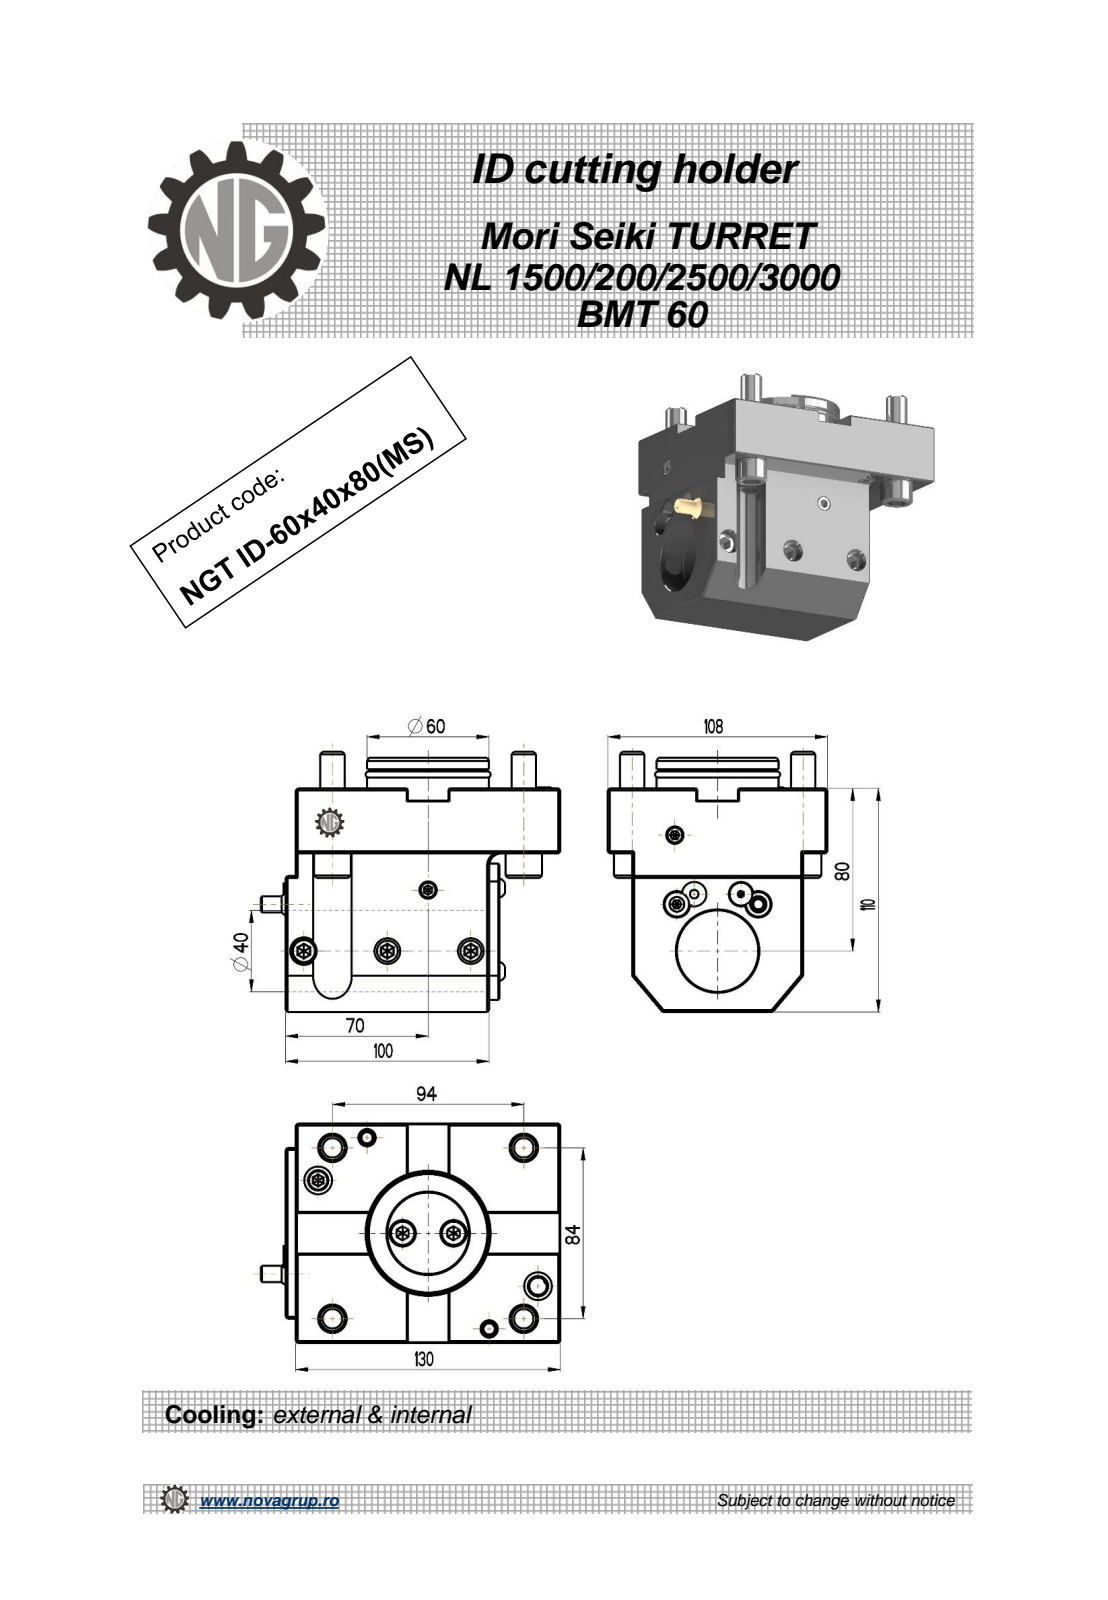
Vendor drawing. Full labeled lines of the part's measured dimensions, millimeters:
Part name (STEP PRODUCT): NGT_ID_60_40_80_MS
STEP written by: PRO/ENGINEER BY PARAMETRIC TECHNOLOGY CORPORATION, 2010280 (CONFIG_CONTROL_DESIGN)
Units: millimetres
Bodies: 2 solids, 646 faces (303 planar, 165 cylindrical, 178 other)
Overall size (bounding box): 147.09 × 128 × 108
Volume: 974 310 mm³ · Surface area: 112 980 mm²
Round holes (diameter × count): ⌀13 ×4, ⌀10.2 ×3, ⌀13.6 ×2, ⌀40 ×2, ⌀5 ×1, ⌀8.5 ×1, ⌀12.5 ×1
Round bosses / shafts (diameter × count): ⌀12 ×5, ⌀18 ×4, ⌀13 ×2, ⌀59.9 ×1, ⌀55.4 ×1, ⌀11.2 ×1, ⌀8 ×1
Partial cylindrical surfaces — rounded edges, fillets, slot ends (radius × count): R0.61 ×36, R0.36 ×20, R0.26 ×12, R0.22 ×6, R0.51 ×6, R9.5 ×2, R4 ×1, R6 ×1
Main face-to-face distances: 12, 96, 5, 100, 110, 32, 78, 84, 108, 6
Hole centre spacings: 63.03, 17.46, 41, 59.93, 68.36, 84, 94, 102.26
